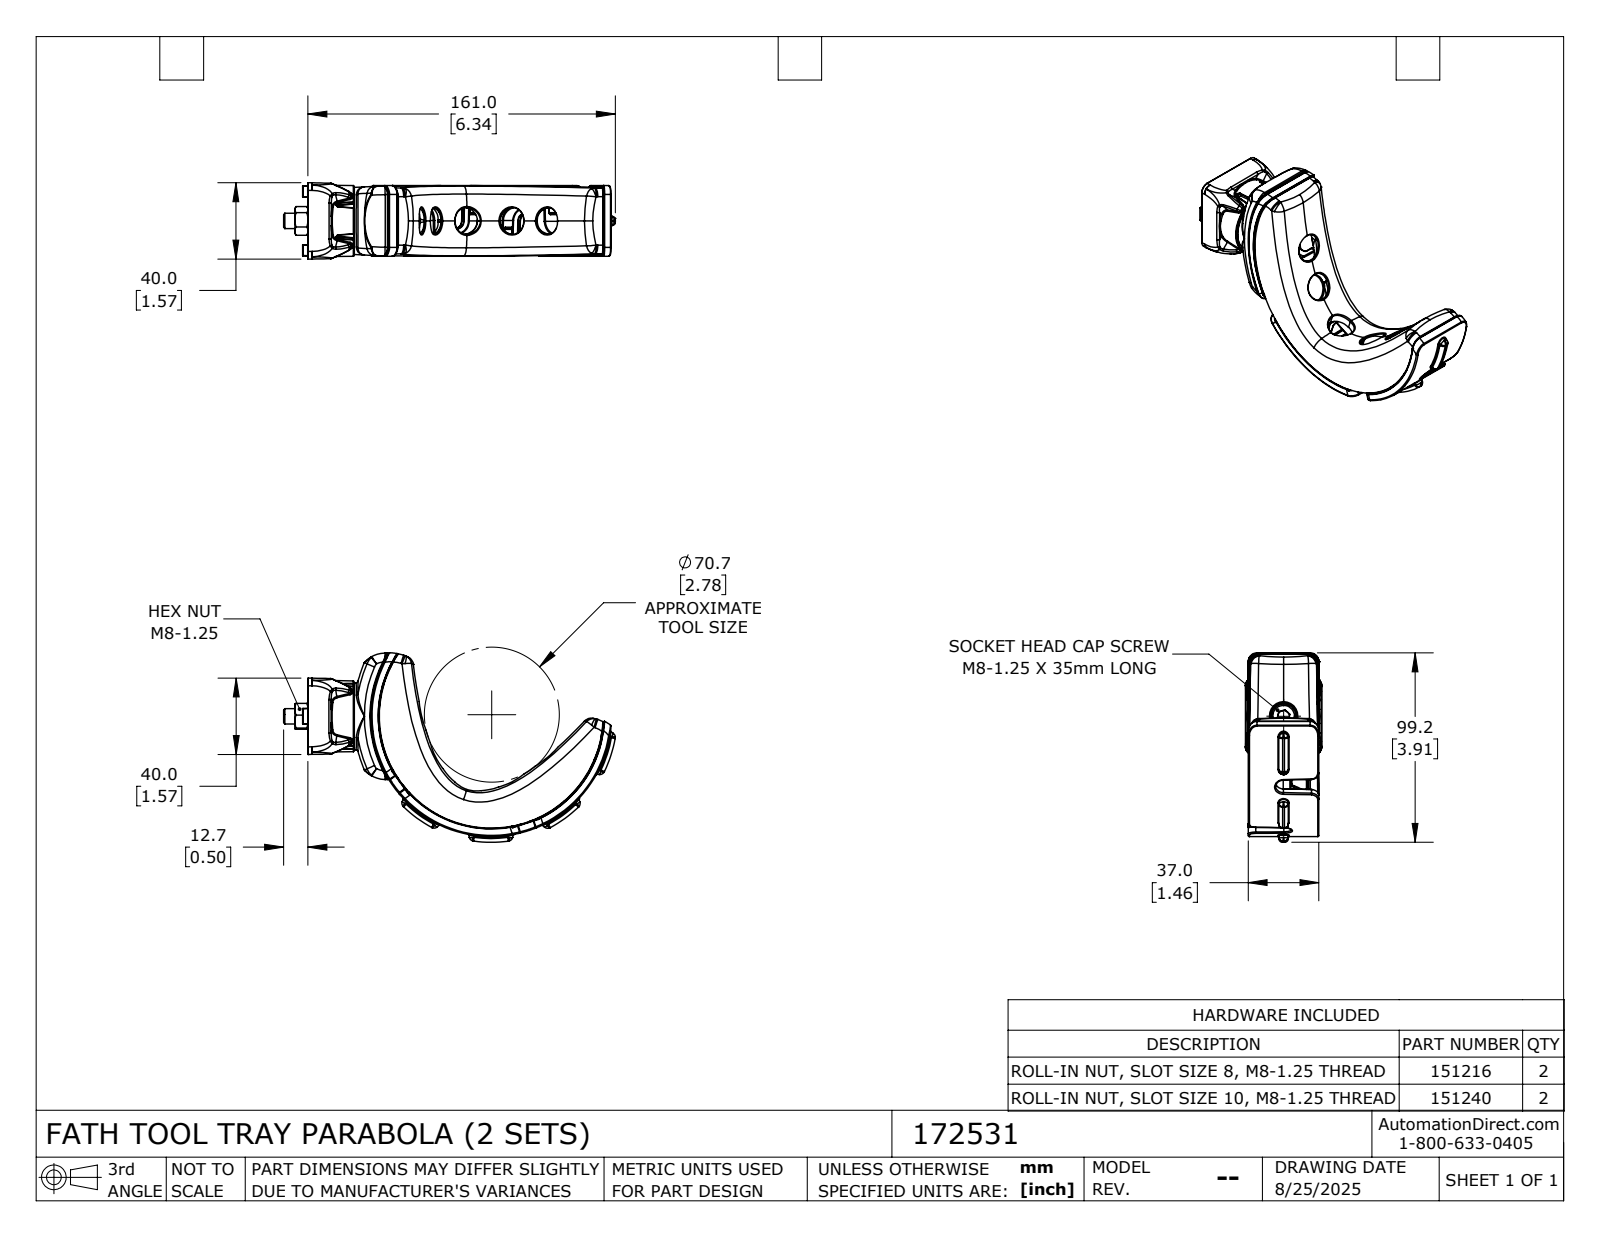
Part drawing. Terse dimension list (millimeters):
name: 172531
written by: SolidWorks 2024 (CONFIG_CONTROL_DESIGN)
unit: mm
bodies: 7 solids, 2075 faces (310 planar, 497 cylindrical, 1268 other)
size: 173.77 × 99.2 × 40
volume: 103 737 mm³; area: 75 257 mm²
holes: 5× ⌀14, 1× ⌀6.8, 1× ⌀7, 1× ⌀8, 1× ⌀13.01
bosses: 1× ⌀31, 1× ⌀13
rounds: 163× R0.2, 32× R0.5, 24× R2.5, 22× R1.2, 18× R4, 14× R1, 14× R6, 10× R0.3
face distances: 24, 8.2, 15.8, 6.5, 14.7, 22.3, 30.5, 13.5, 7.6, 13.33
